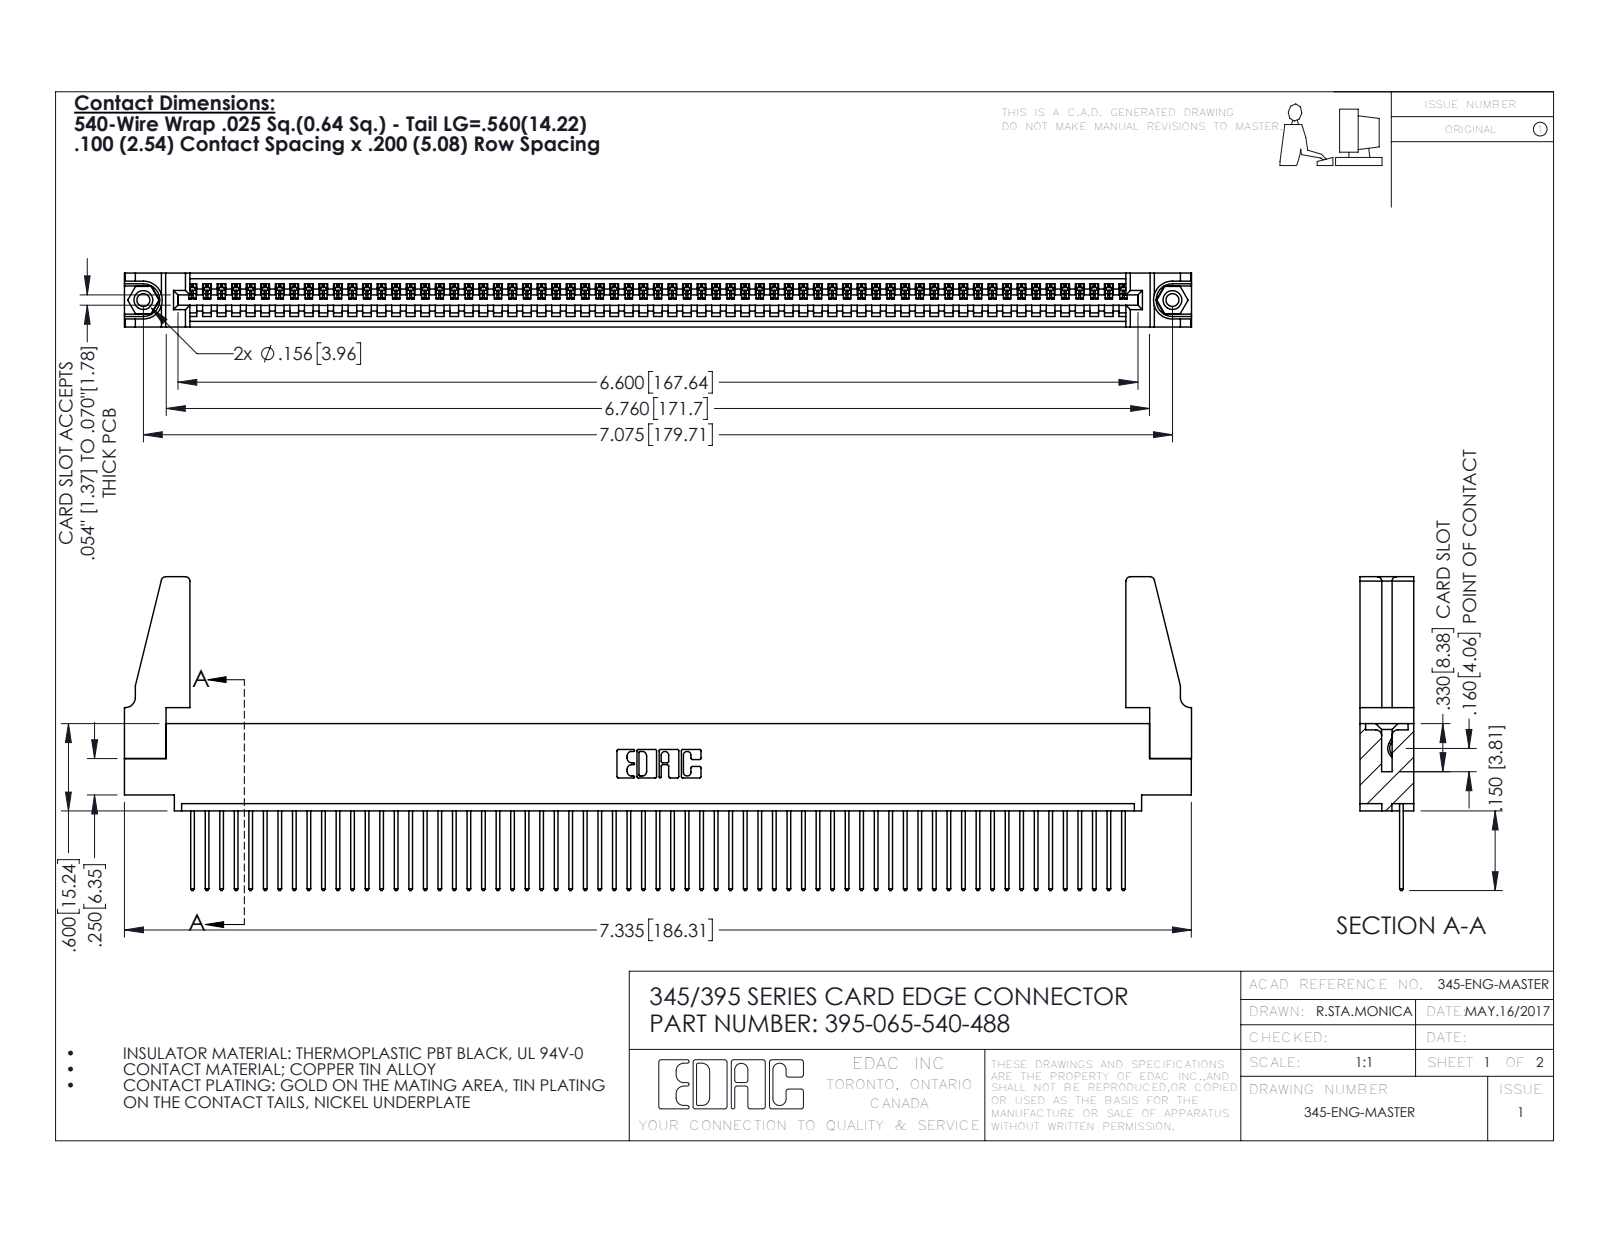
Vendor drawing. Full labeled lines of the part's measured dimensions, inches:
Part name (STEP PRODUCT): 345-250-001_345-250-001-102; 345 Part_0.110 Offset - 0.156 Dia-TH; 345-292-001_345-293-140; 345-220-078_345-220-088 (+1 more)
STEP written by: SolidWorks 2016 (CONFIG_CONTROL_DESIGN)
Units: inches
Bodies: 70 solids, 4024 faces (2756 planar, 1252 cylindrical, 16 other)
Overall size (bounding box): 7.336 × 2.157 × 0.37
Volume: 1.291 in³ · Surface area: 43.32 in²
Round holes (diameter × count): ⌀0.089 ×2, ⌀0.125 ×2, ⌀0.156 ×2, ⌀0.064 ×1
Round bosses / shafts (diameter × count): ⌀0.155 ×2
Partial cylindrical surfaces — rounded edges, fillets, slot ends (radius × count): R0.006 ×130, R0.01 ×130, R0.01 ×22, R0.03 ×8, R0.007 ×6, R0.031 ×6, R0.026 ×3, R0.031 ×2
Main face-to-face distances: 0.072, 0.298, 0.37, 0.098, 0.272, 0.025, 0.2, 0.225, 0.149, 0.072
Hole centre spacings: 0.27, 6.839, 7.075
